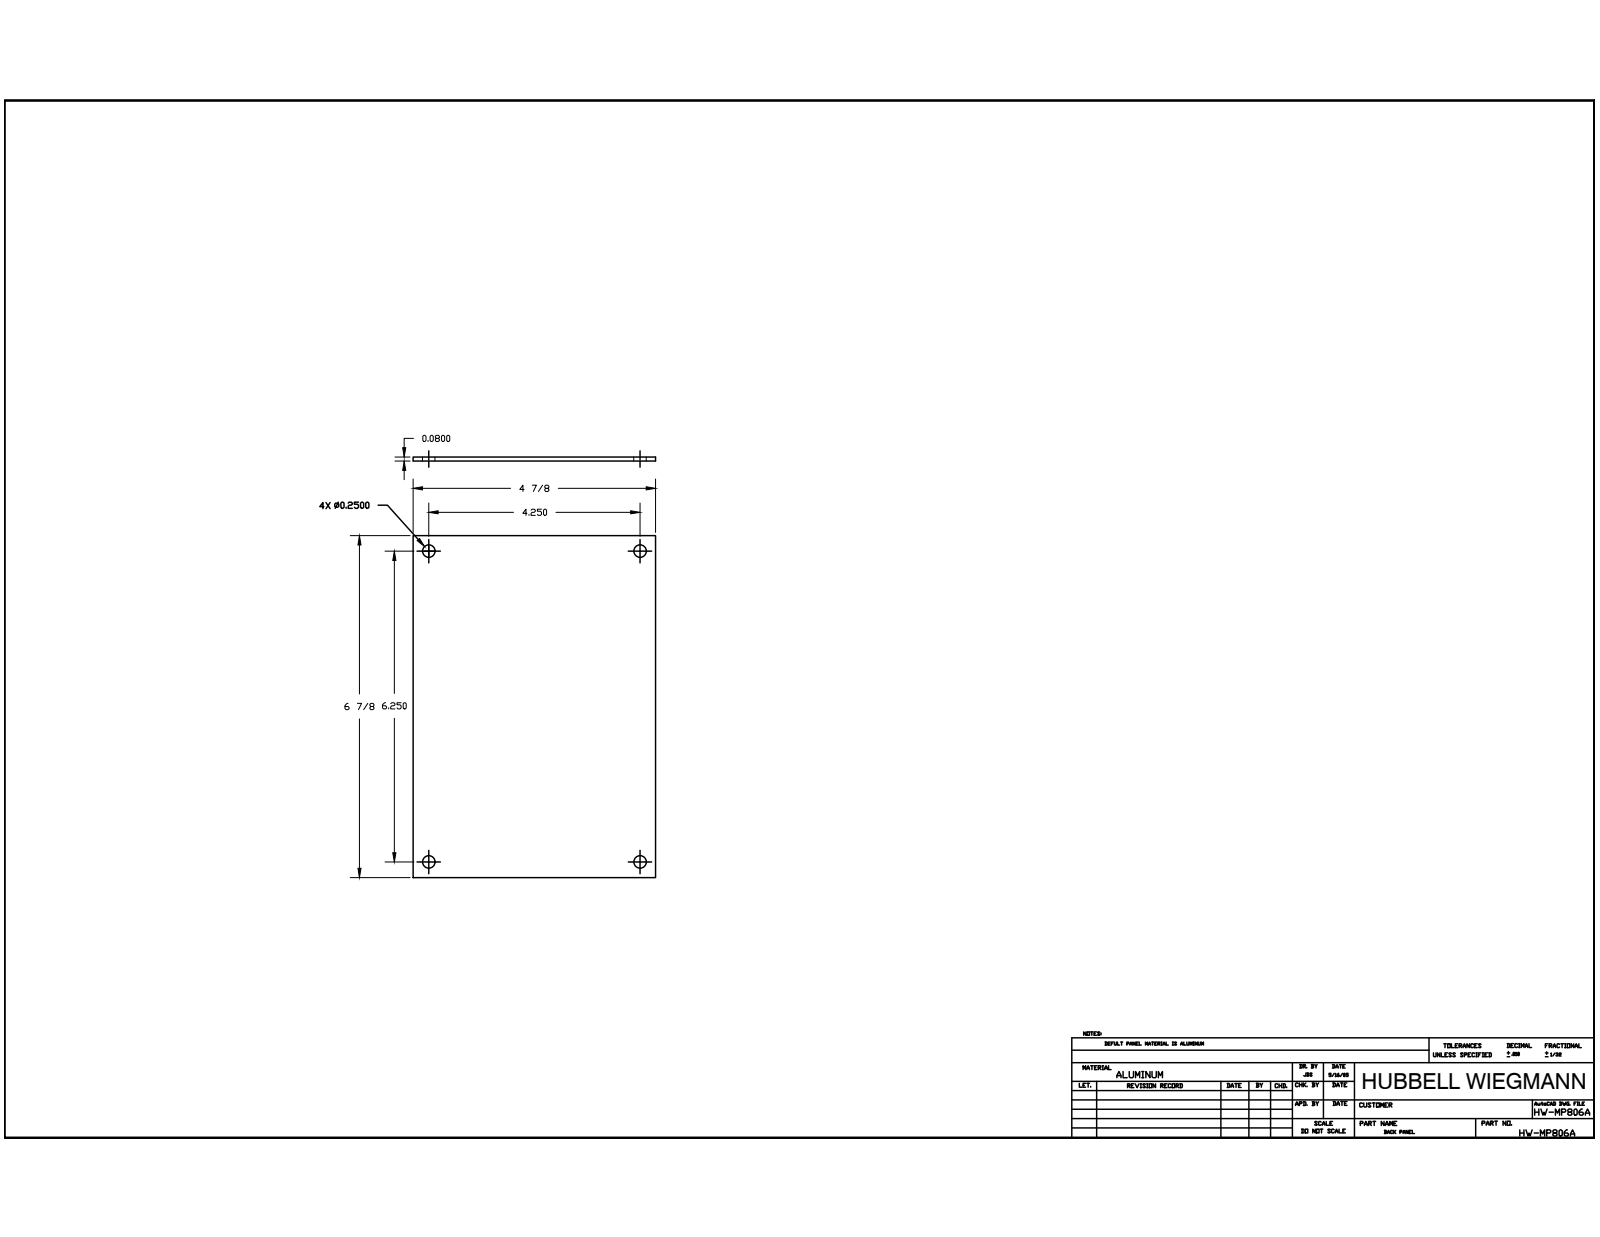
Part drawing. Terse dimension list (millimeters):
name: BP86AL_STP
written by: Autodesk Inventor 2014 (AUTOMOTIVE_DESIGN)
unit: mm
bodies: 1 solid, 10 faces (6 planar, 4 cylindrical, 0 other)
size: 174.62 × 123.83 × 2.03
volume: 43 680 mm³; area: 44 368 mm²
holes: 4× ⌀6.35
face distances: 2.03, 123.82, 174.62
hole spacings: 107.94, 158.76, 191.98
